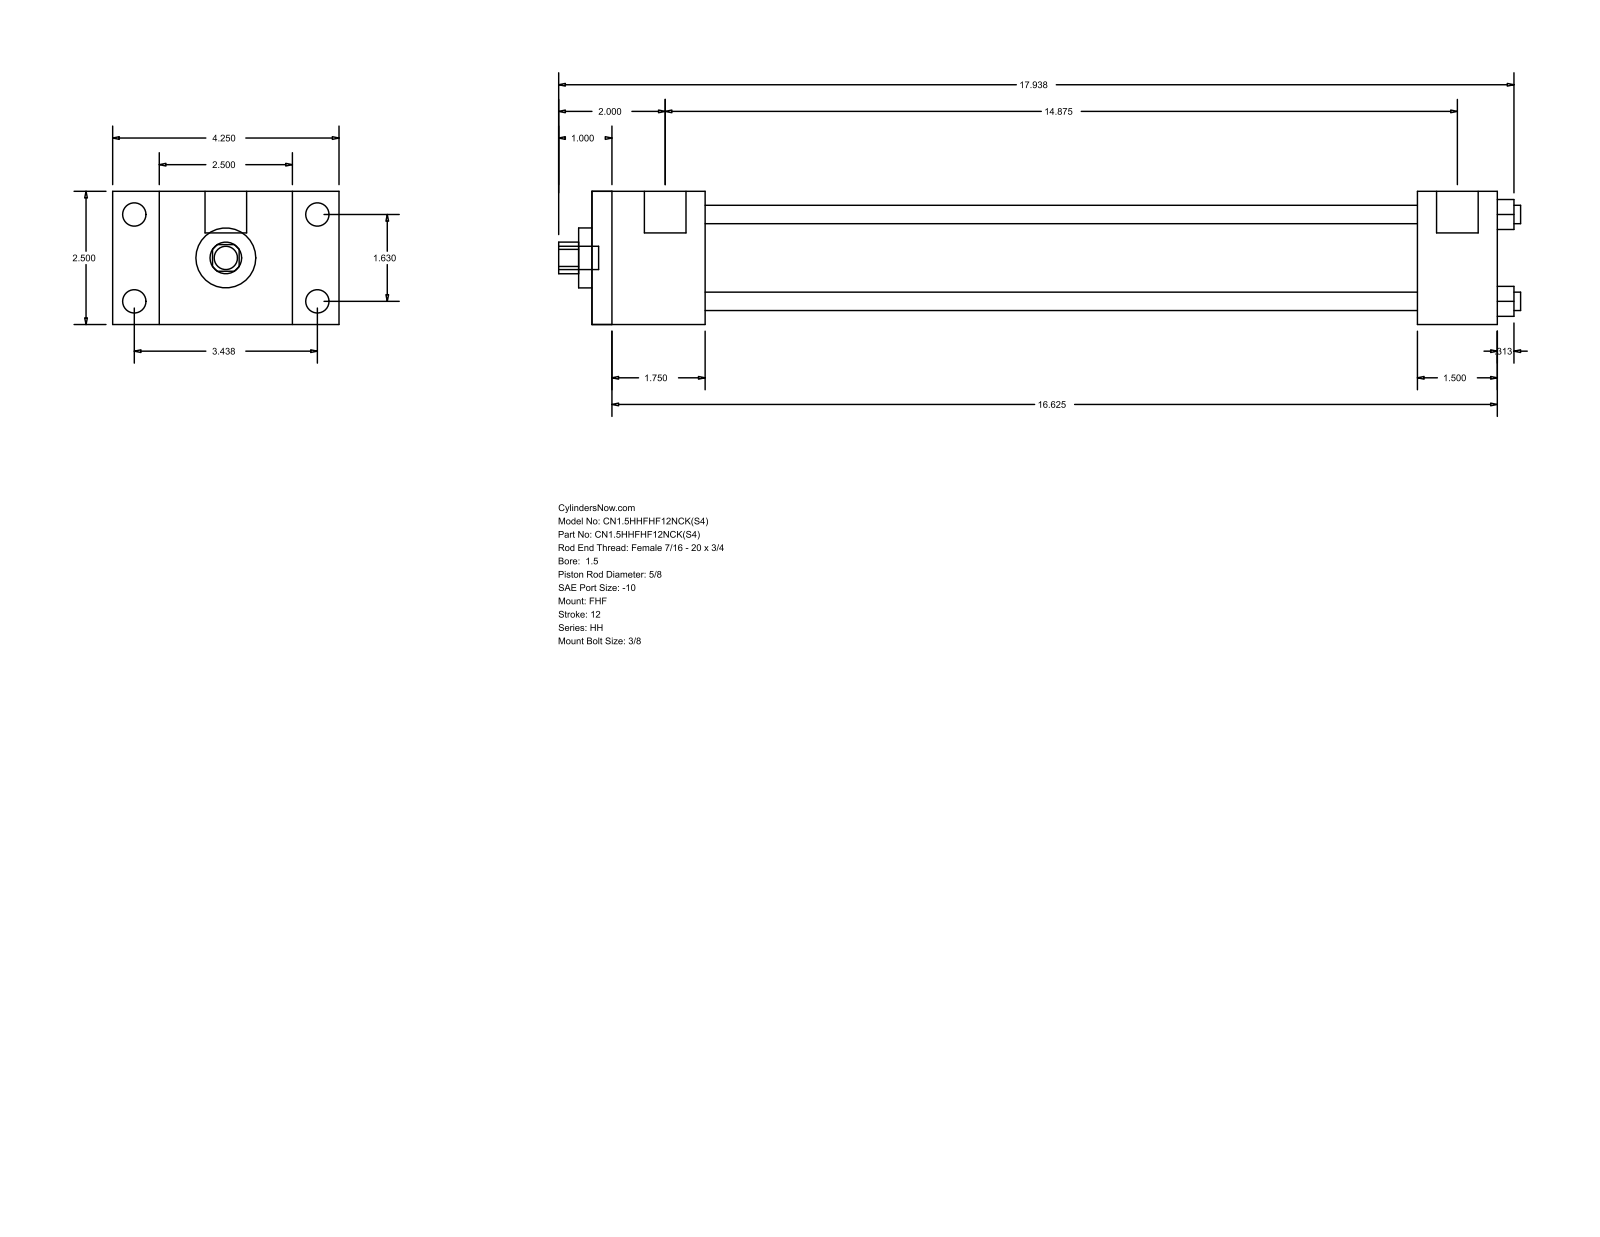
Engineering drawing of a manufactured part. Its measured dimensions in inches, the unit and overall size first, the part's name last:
Units: inches
Overall size (bounding box): 18.063 × 4.25 × 2.5
Round holes (diameter × count): ⌀0.345 ×4, ⌀0.625 ×1, ⌀1.125 ×1, ⌀1.75 ×1
Round bosses / shafts (diameter × count): ⌀0.438 ×4, ⌀0.219 ×4, ⌀0.781 ×2, ⌀0.437 ×1
Partial cylindrical surfaces — rounded edges, fillets, slot ends (radius × count): R0.297 ×1
Main face-to-face distances: 2.5, 0.875, 3.375, 2.125, 4.25, 17, 14.875, 15.5, 13.375, 1.5
Hole centre spacings: 1.152, 1.63, 2.305
Bodies: 0 solids, 88 faces (60 planar, 28 cylindrical, 0 other)
Part name (STEP PRODUCT): HH_FHF__0150_0.625
STEP written by: GSSL Pune (CONFIG_CONTROL_DESIGN)
